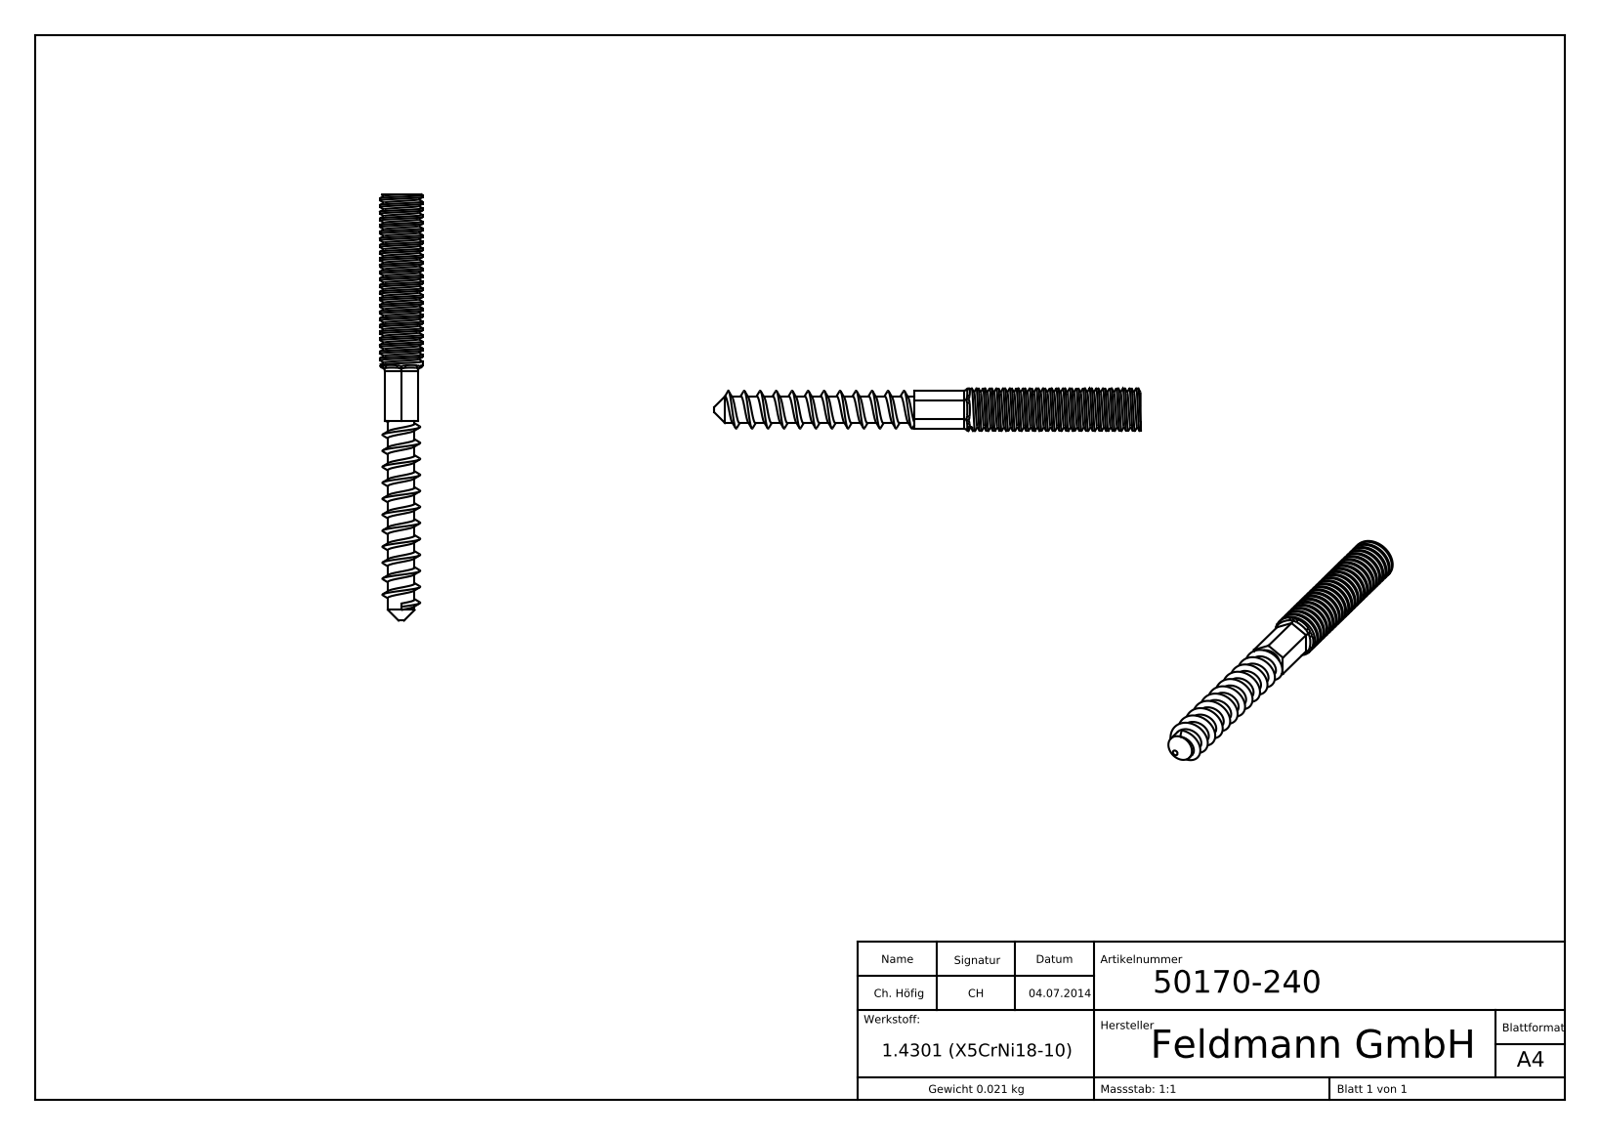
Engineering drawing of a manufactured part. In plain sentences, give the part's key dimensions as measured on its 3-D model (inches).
The part is named "50170-240". Its 3-D file was written by "SolidWorks 2015 (CONFIG_CONTROL_DESIGN)". It is 1 solid with 235 faces: 78 planar, 79 cylindrical and 78 other. Overall it measures 3.15 by 0.315 by 0.315 inches. Its volume is 0.16 cubic inches and its surface area 3.829 square inches. Round bosses or shafts: 1 of diameter 0.315, 1 of diameter 0.197. The main face-to-face distances are 0.242, 1.673, 0.121, 0.02, 1.654, 3.15, 3.13, 1.476, 0.016, 0.013.
